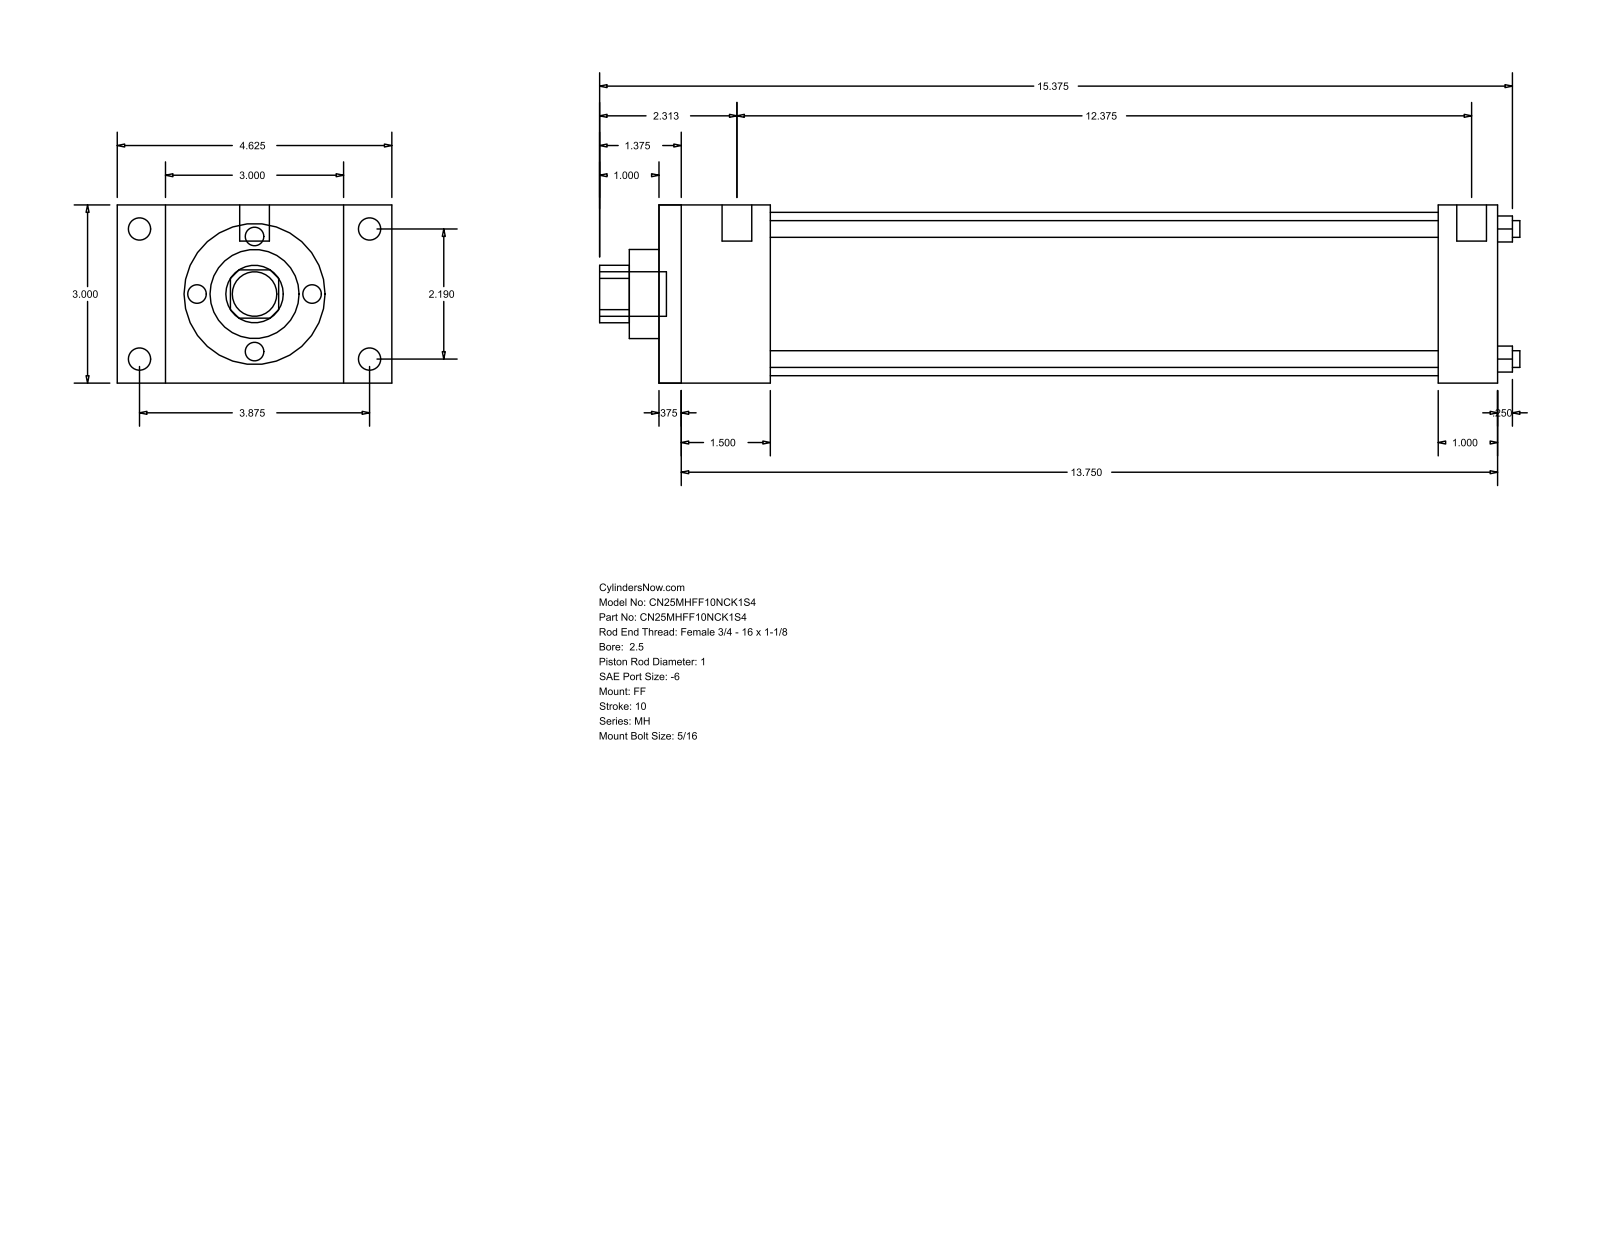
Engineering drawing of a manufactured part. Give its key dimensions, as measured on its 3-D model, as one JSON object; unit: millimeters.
{"part_name": "MH_FF__0250_1", "step_written_by": "GSSL Pune (CONFIG_CONTROL_DESIGN)", "units": "millimeters", "bodies": {"solids": 0, "faces": 92, "planar": 64, "cylindrical": 28, "other": 0}, "overall_size": [393.7, 117.47, 76.2], "round_holes": [[7.14, 4], [25.4, 1], [38.1, 1], [69.85, 1]], "round_bosses_or_shafts": [[9.53, 4], [5.56, 4], [12.7, 2], [19.05, 1]], "partial_cylinders_radius": [[12.29, 1]], "face_to_face_distances": [76.2, 358.78, 9.52, 349.26, 47.63, 333.37, 38.11, 323.85, 285.74, 311.15], "hole_center_spacings": [39.33, 55.62, 78.66]}
